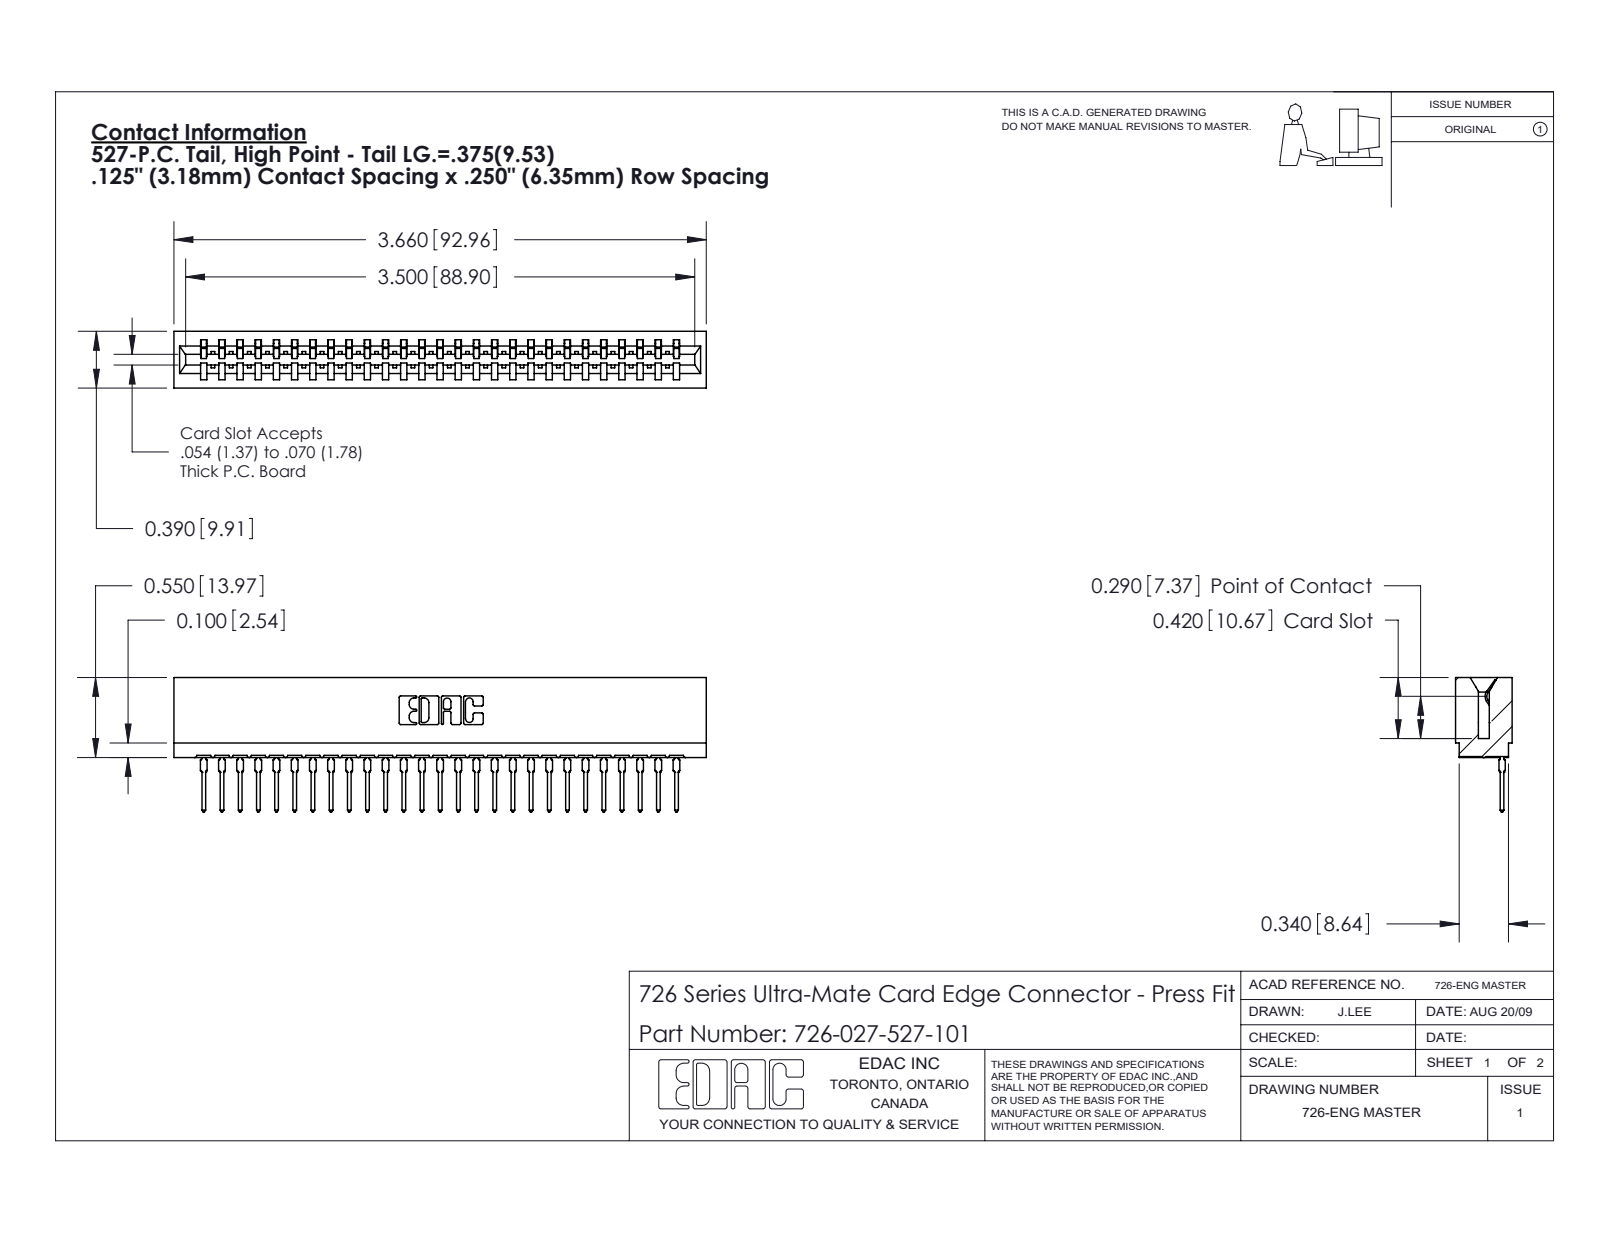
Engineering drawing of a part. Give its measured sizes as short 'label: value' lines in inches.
name: 726 Part_.515 Slot Depth - 01; 746-292-001_527; 726-027-527-101
written by: SolidWorks 2020 (CONFIG_CONTROL_DESIGN)
unit: in
bodies: 28 solids, 3013 faces (1756 planar, 555 cylindrical, 702 other)
size: 3.66 × 0.924 × 0.39
volume: 0.513 in³; area: 19.8 in²
rounds: 54× R0.021, 28× R0.015, 22× R0.01, 6× R0.007, 6× R0.031, 4× R0.005, 4× R0.011, 3× R0.026
face distances: 0.057, 0.333, 0.39, 0.25, 0.025, 0.307, 0.083, 0.275, 0.5, 0.365
